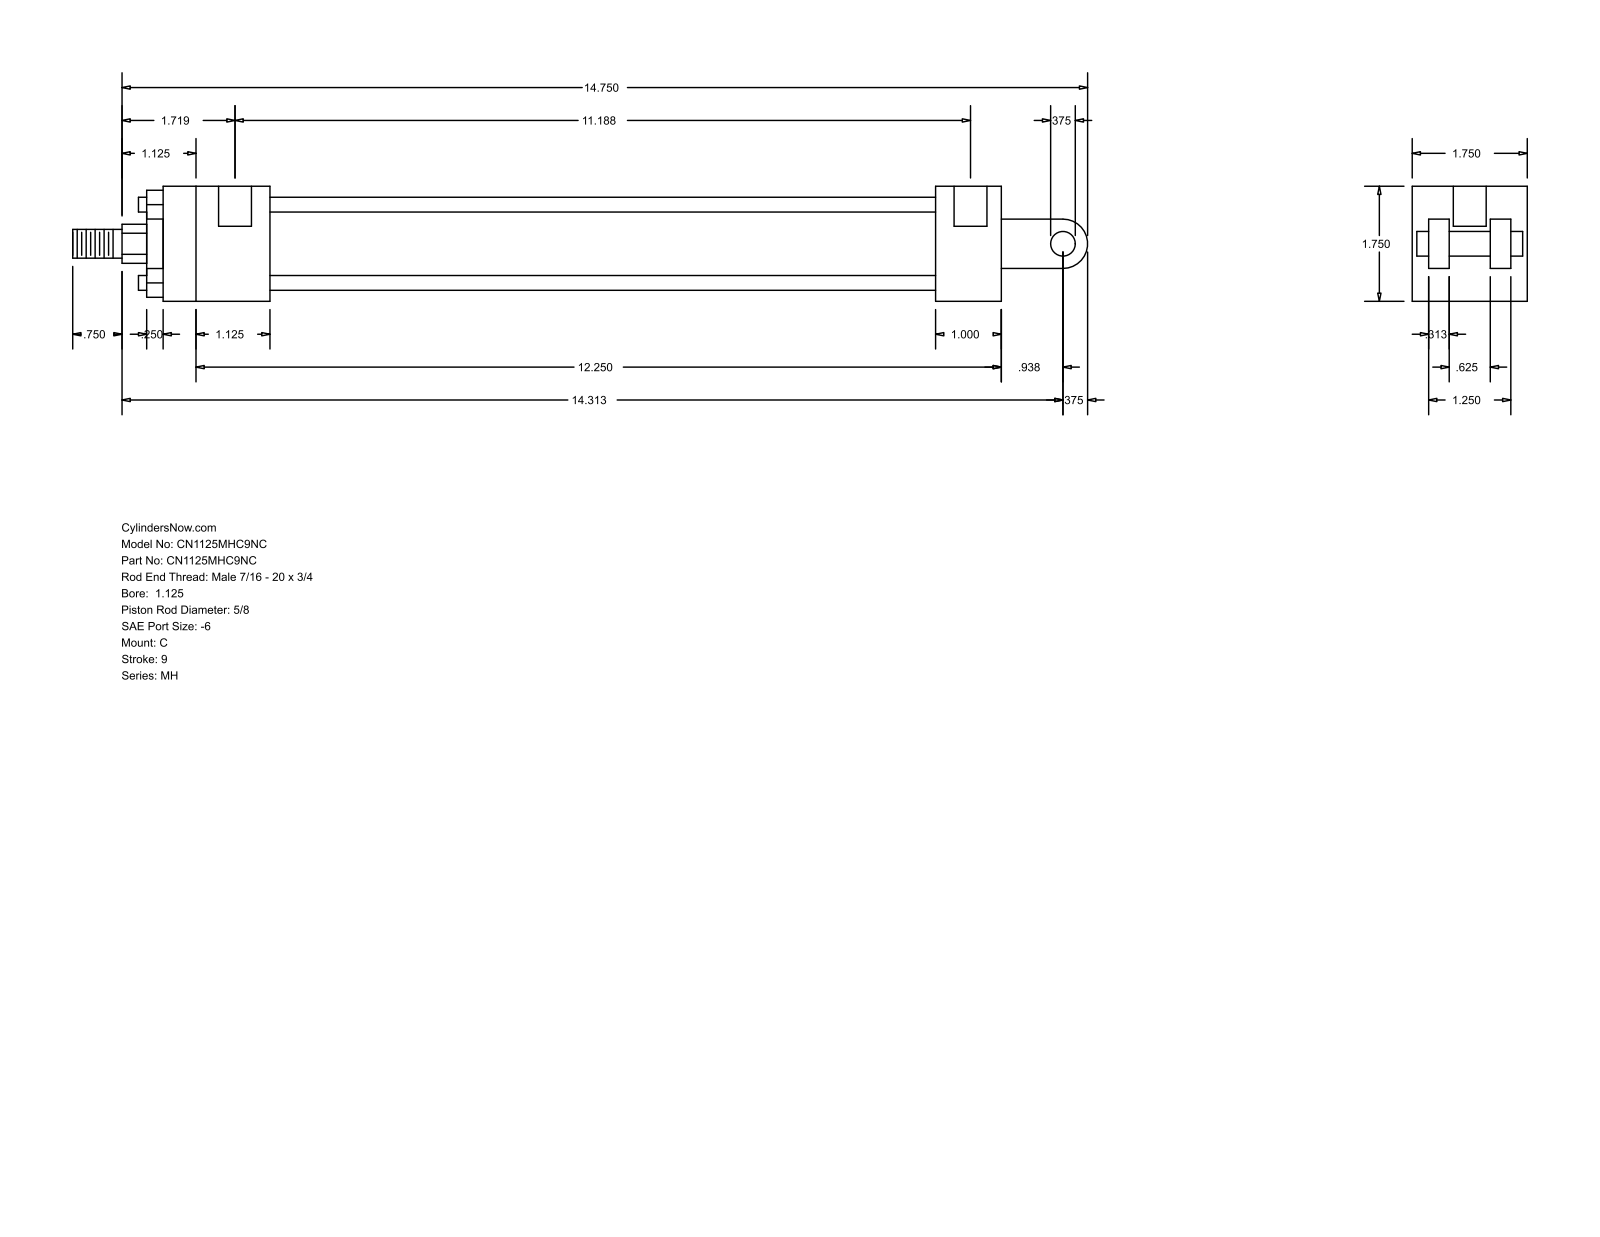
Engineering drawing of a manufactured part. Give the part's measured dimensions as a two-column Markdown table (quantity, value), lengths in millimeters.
| quantity | value |
| --- | --- |
| part name | MH_C__0112_0.625 |
| STEP written by | GSSL Pune (CONFIG_CONTROL_DESIGN) |
| units | millimeters |
| bodies | 0 solids, 99 faces (70 planar, 29 cylindrical, 0 other) |
| overall size | 392.11 × 44.45 × 44.45 |
| round holes (diameter × count) | 5.56 × 4, 12.7 × 2 |
| round bosses / shafts (diameter × count) | 5.71 × 4, 34.92 × 1, 28.57 × 1, 15.88 × 1, 11.11 × 1, 9.53 × 1 |
| partial cylindrical surfaces (radius × count) | 7.54 × 1, 9.53 × 1 |
| main face-to-face distances | 44.46, 6.35, 31.76, 14.29, 30.17, 38.11, 7.94, 23.82, 41.27, 12.7 |
| hole center spacings | 280.99, 3.17, 284.16 |
